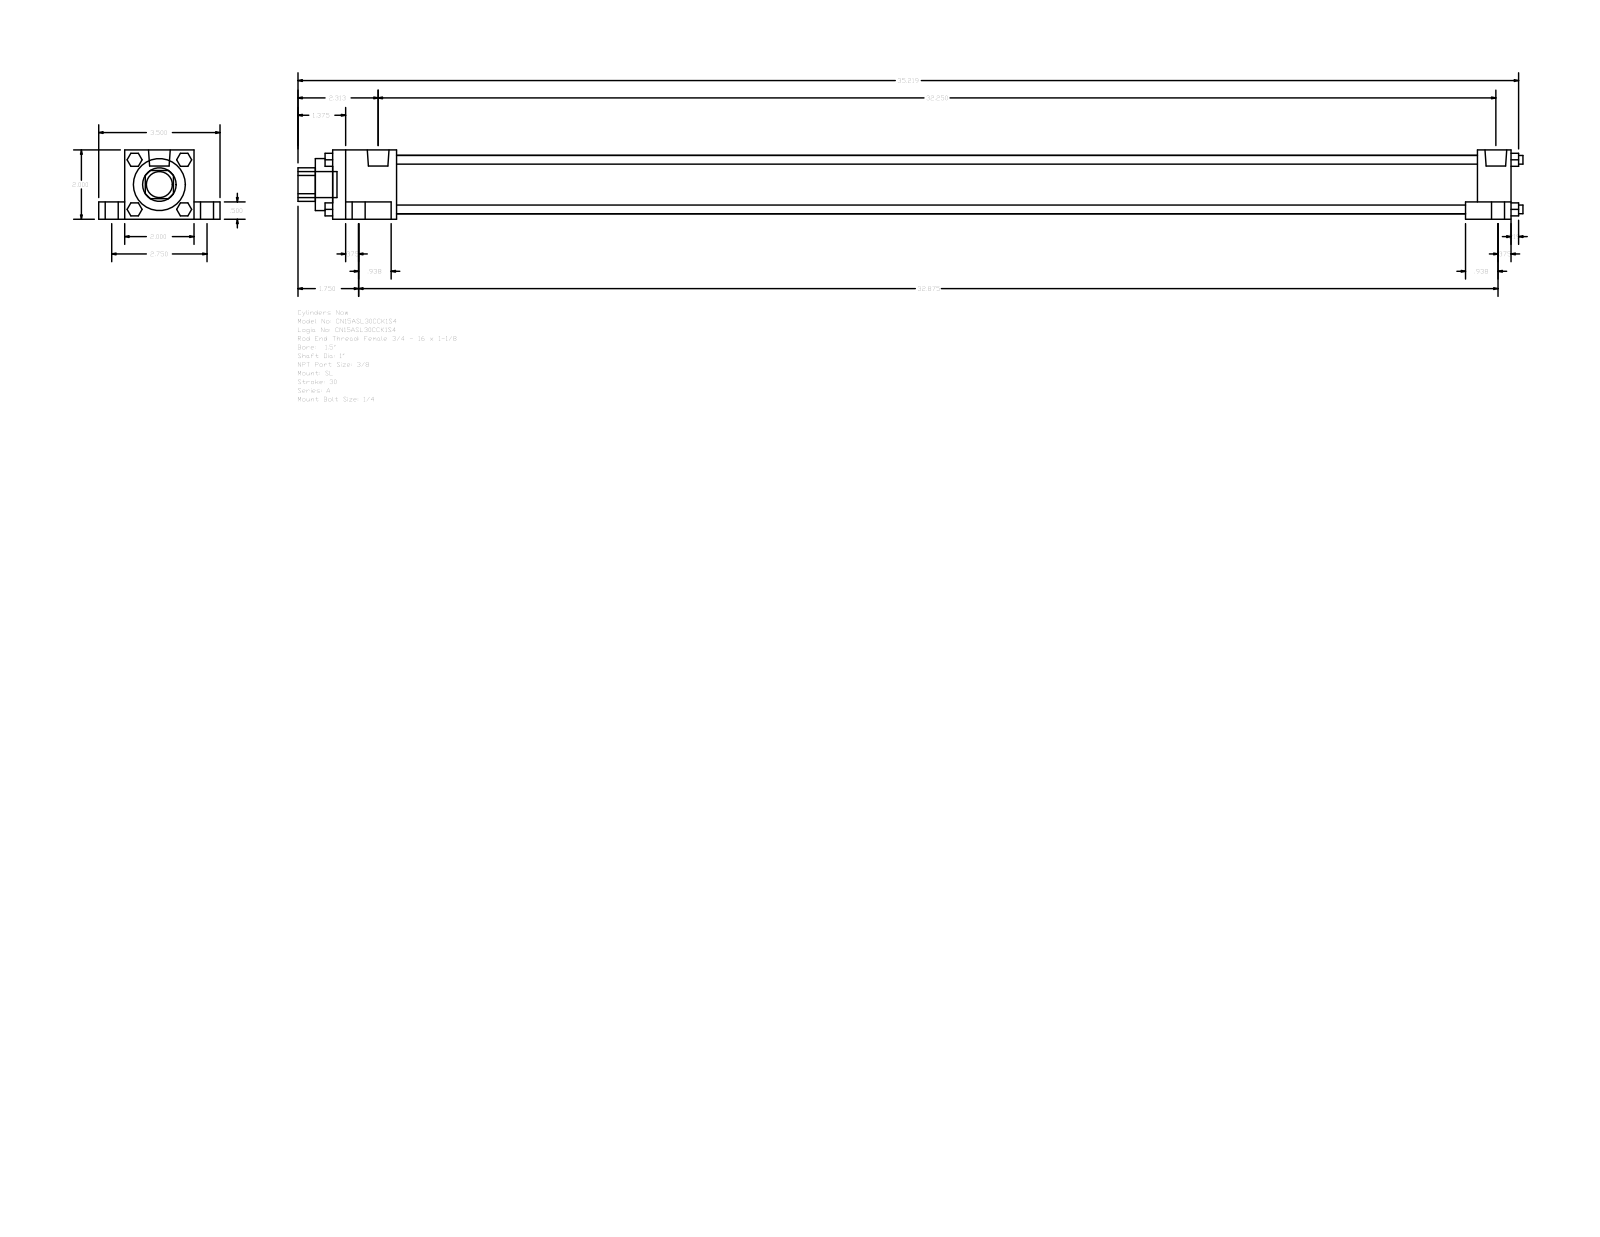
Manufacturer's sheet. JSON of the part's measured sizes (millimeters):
{"part_name": "A_SL__0150_1", "step_written_by": "GSSL Pune (CONFIG_CONTROL_DESIGN)", "units": "millimeters", "bodies": {"solids": 0, "faces": 148, "planar": 112, "cylindrical": 36, "other": 0}, "overall_size": [897.73, 88.9, 50.8], "round_holes": [[25.4, 1], [38.1, 1], [42.93, 1]], "round_bosses_or_shafts": [[15.88, 4], [9.53, 4], [6.35, 4], [5.56, 4], [15.93, 2], [19.05, 1]], "partial_cylinders_radius": [[12.29, 1]], "face_to_face_distances": [50.8, 12.7, 38.1, 19.05, 69.85, 9.52, 863.6, 33.34, 838.99, 24.61]}
